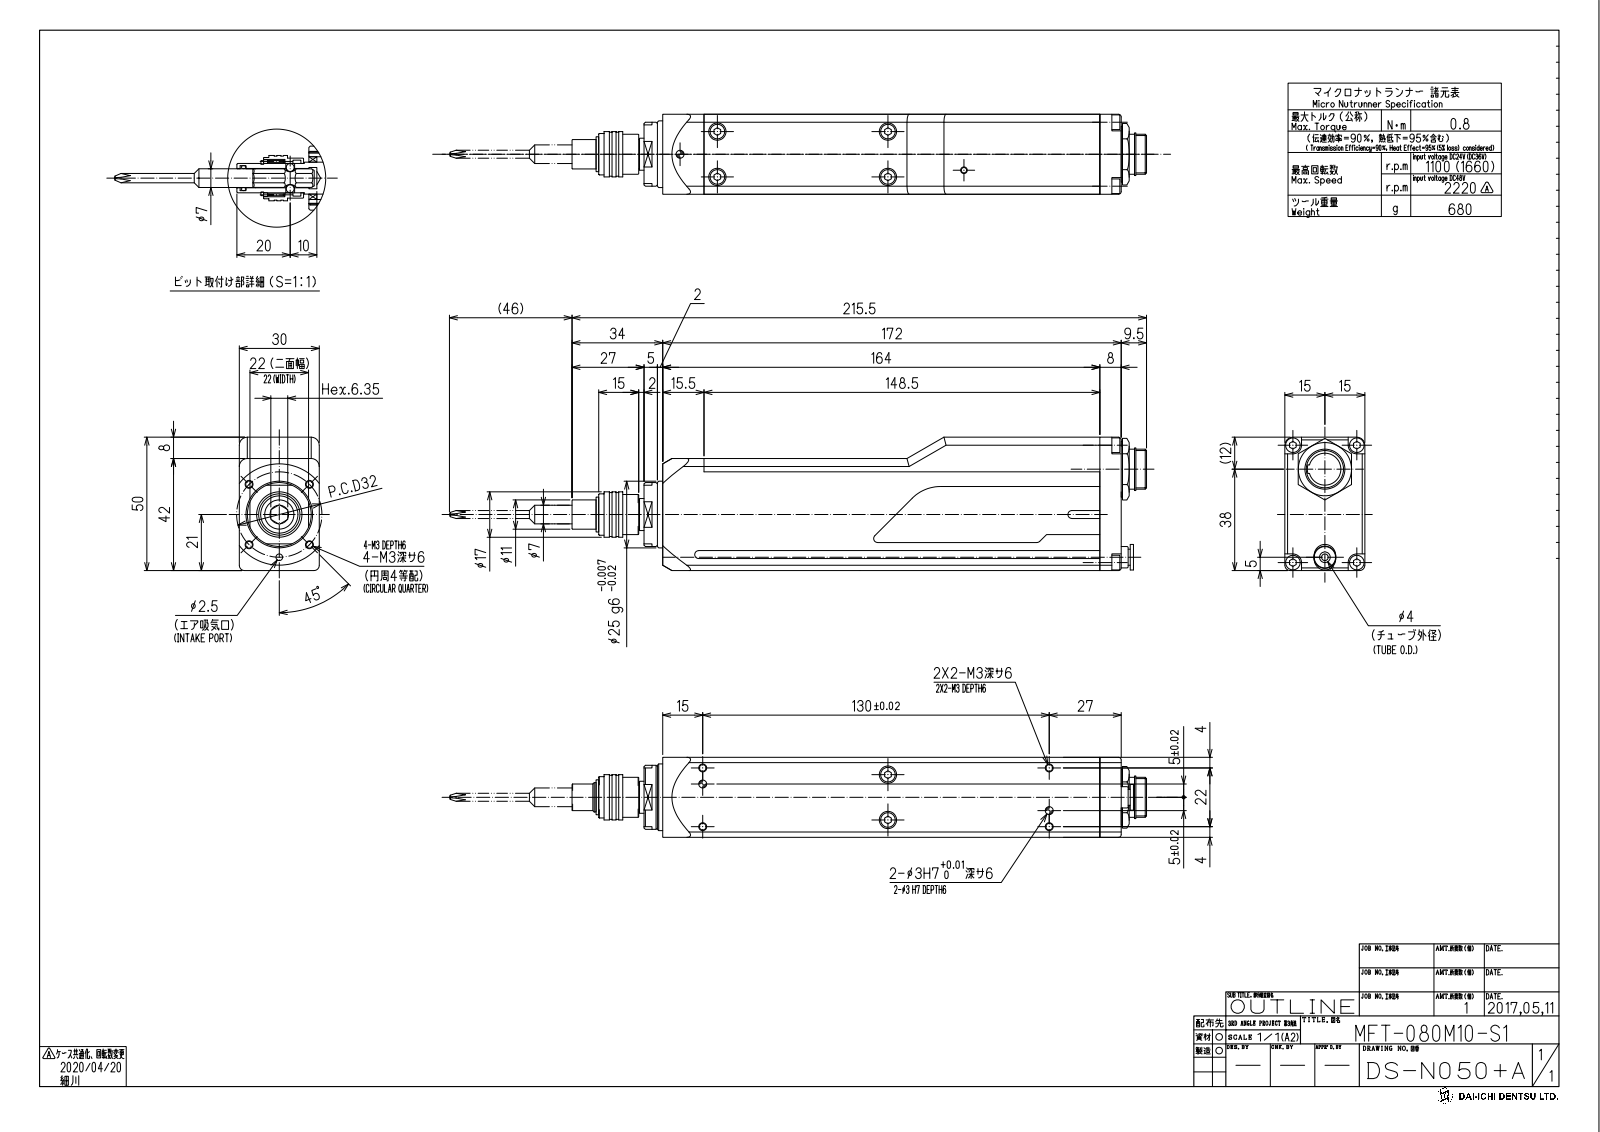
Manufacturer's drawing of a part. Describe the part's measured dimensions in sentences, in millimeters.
The part is named "MFT-080M10-S1". Its 3-D file was written by "SolidWorks 2017 (AUTOMOTIVE_DESIGN)". It is 5 solids with 396 faces: 204 planar, 141 cylindrical and 51 other. Overall it measures 215.5 by 50 by 30 millimeters. Its volume is 237 484 cubic millimeters and its surface area 45 412 square millimeters. Round holes: 5 of diameter 2.5, 4 of diameter 1.6, 4 of diameter 6, 2 of diameter 3, 2 of diameter 6.5, 1 of diameter 3.5, 1 of diameter 5, 1 of diameter 7, 1 of diameter 12. Round bosses or shafts: 10 of diameter 5.5, 2 of diameter 15, 1 of diameter 25, 1 of diameter 24, 1 of diameter 20, 1 of diameter 17, 1 of diameter 16, 1 of diameter 15.5. Partial cylindrical surfaces (rounded edges, fillets, slot ends): 9 of radius 3, 4 of radius 1.5, 2 of radius 1, 1 of radius 7, 1 of radius 11.54, 1 of radius 15. The main face-to-face distances are 30, 0.5, 29.5, 37, 37.01, 8, 5, 29, 42, 4.99. The hole center spacings are 15.99, 17, 22.62, 60.55, 63.56, 69.54, 72.18, 16.
